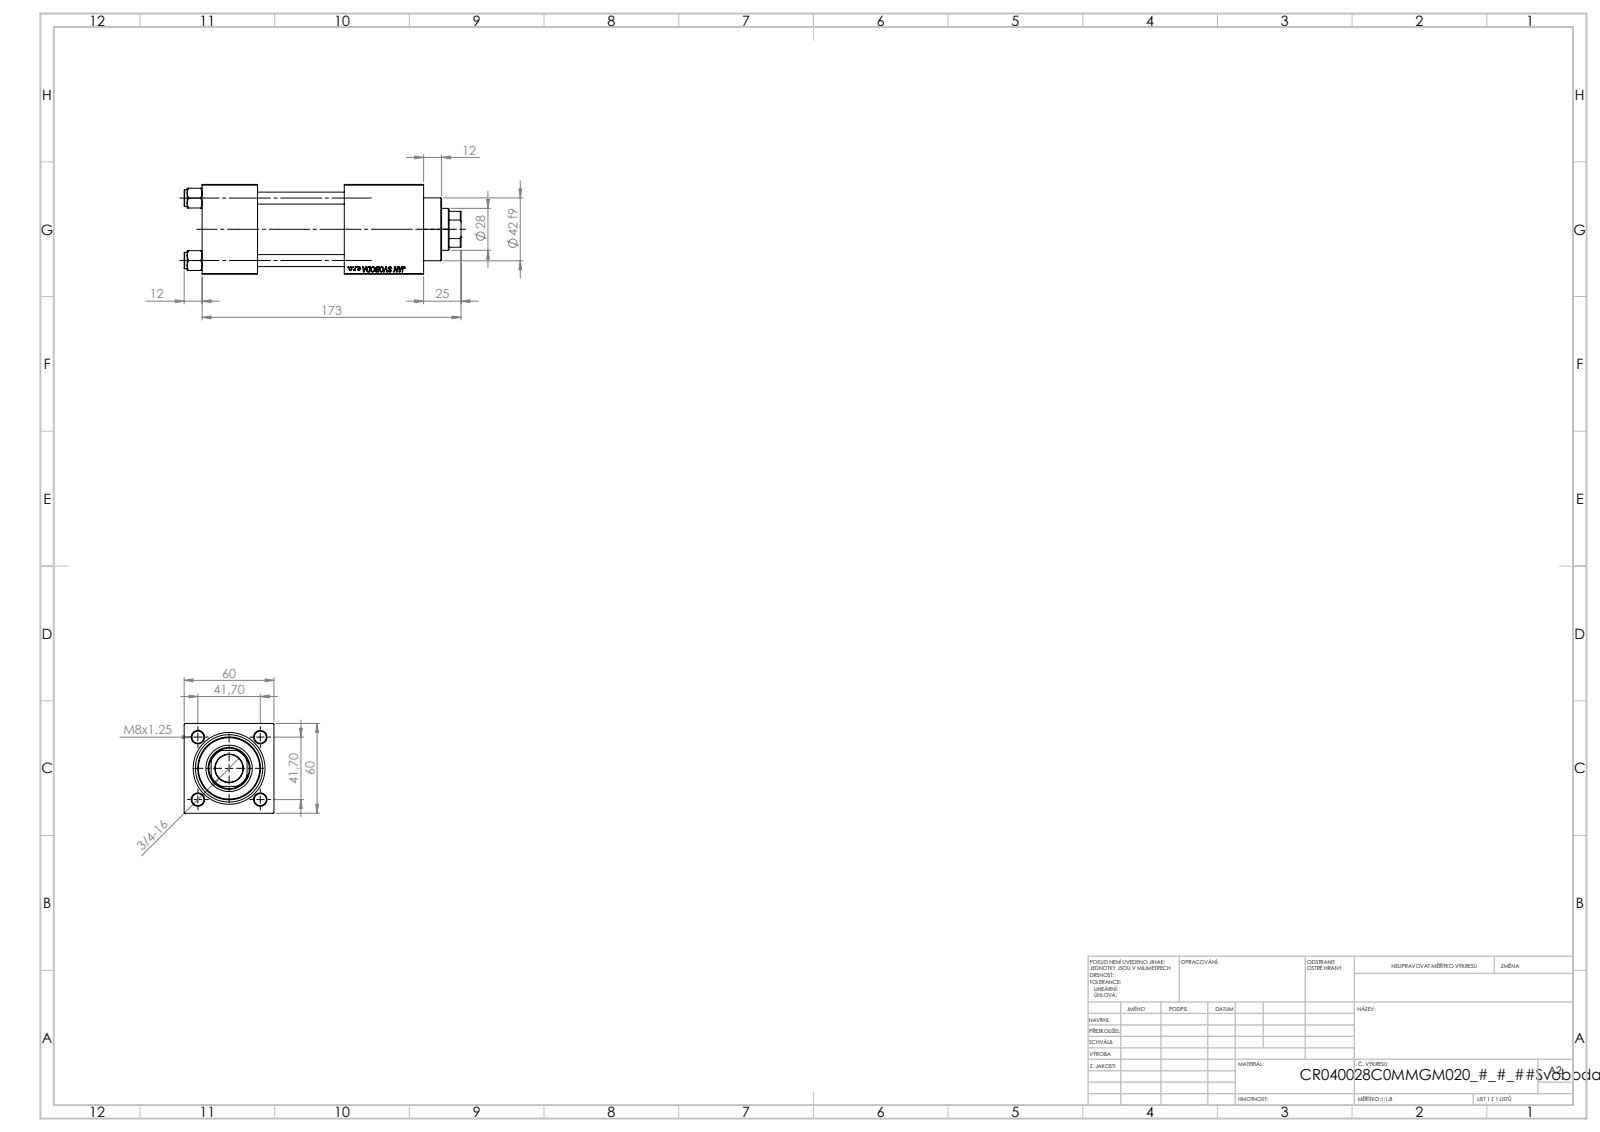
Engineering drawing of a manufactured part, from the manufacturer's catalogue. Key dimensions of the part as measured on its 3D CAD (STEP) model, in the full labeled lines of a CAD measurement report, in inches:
Part name (STEP PRODUCT): V215CR_VCP_C; NUT_M5_C; V215CR_C_TYCINKA; V215CR_C_Body (+1 more)
STEP written by: SolidWorks 2019 (CONFIG_CONTROL_DESIGN)
Units: inches
Bodies: 11 solids, 1148 faces (526 planar, 86 cylindrical, 536 other)
Overall size (bounding box): 7.283 × 2.362 × 2.362
Volume: 25.9 in³ · Surface area: 172.6 in²
Round holes (diameter × count): ⌀0.315 ×4, ⌀0.276 ×2, ⌀0.656 ×2, ⌀0.945 ×2, ⌀0.728 ×1, ⌀1.102 ×1, ⌀1.22 ×1, ⌀1.575 ×1, ⌀1.772 ×1
Round bosses / shafts (diameter × count): ⌀0.433 ×4, ⌀1.811 ×1, ⌀1.654 ×1
Partial cylindrical surfaces — rounded edges, fillets, slot ends (radius × count): R0.531 ×1
Main face-to-face distances: 2.362, 1.457, 2.283, 3.74, 2.087, 4.697, 3.24, 0.957, 5.827, 4.37
Hole centre spacings: 1.161, 1.642, 2.322, 3.642
